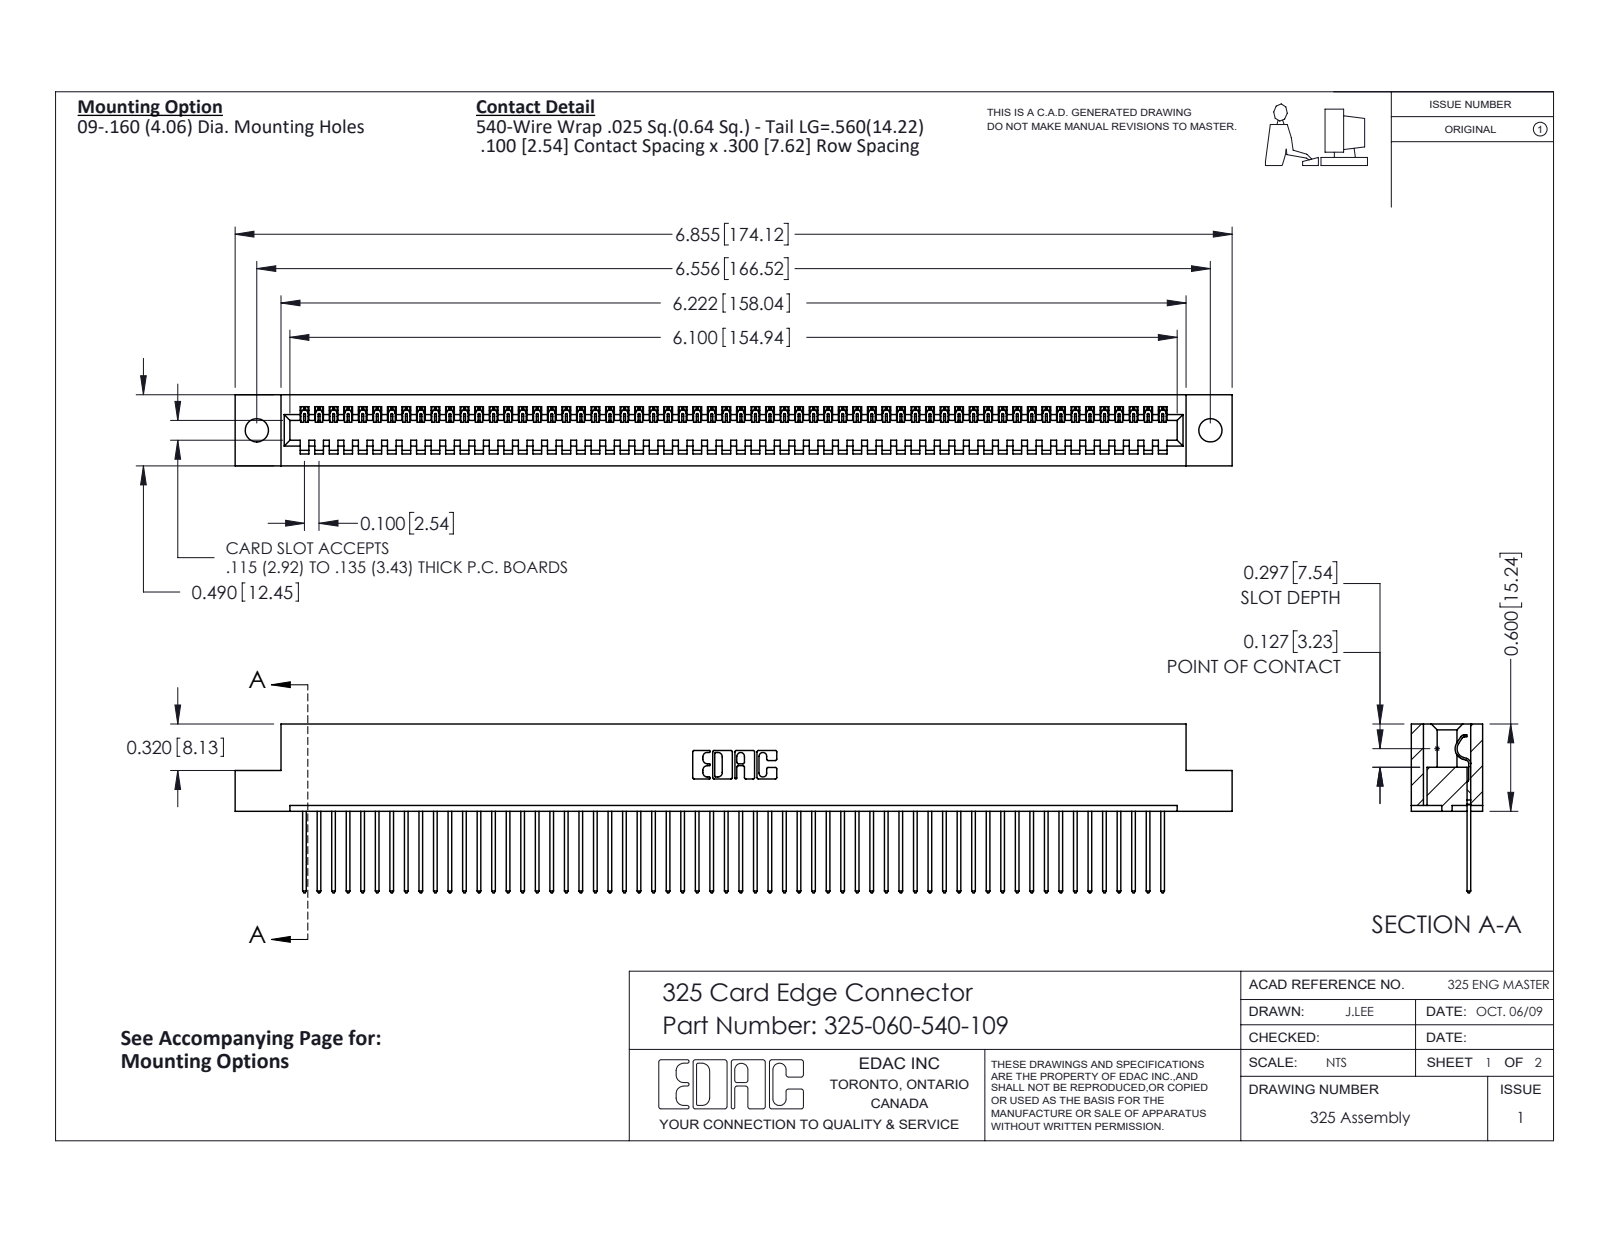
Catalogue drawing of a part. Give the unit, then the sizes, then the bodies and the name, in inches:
Units: inches
Overall size (bounding box): 6.855 × 1.16 × 0.49
Round holes (diameter × count): ⌀0.16 ×2
Partial cylindrical surfaces — rounded edges, fillets, slot ends (radius × count): R0.006 ×120, R0.01 ×120, R0.01 ×22, R0.007 ×6, R0.031 ×6, R0.026 ×3, R0.014 ×1, R0.022 ×1
Main face-to-face distances: 0.083, 0.407, 0.49, 0.3, 0.107, 0.383, 0.025, 0.325, 0.56, 0.263
Hole centre spacings: 6.556
Volume: 1.348 in³ · Surface area: 38.66 in²
Bodies: 61 solids, 3594 faces (2590 planar, 1004 cylindrical, 0 other)
Part name (STEP PRODUCT): 325-060-540-109; 325 Part_.160 TH; 325-292-001_325-293-140
STEP written by: SolidWorks 2016 (CONFIG_CONTROL_DESIGN)
